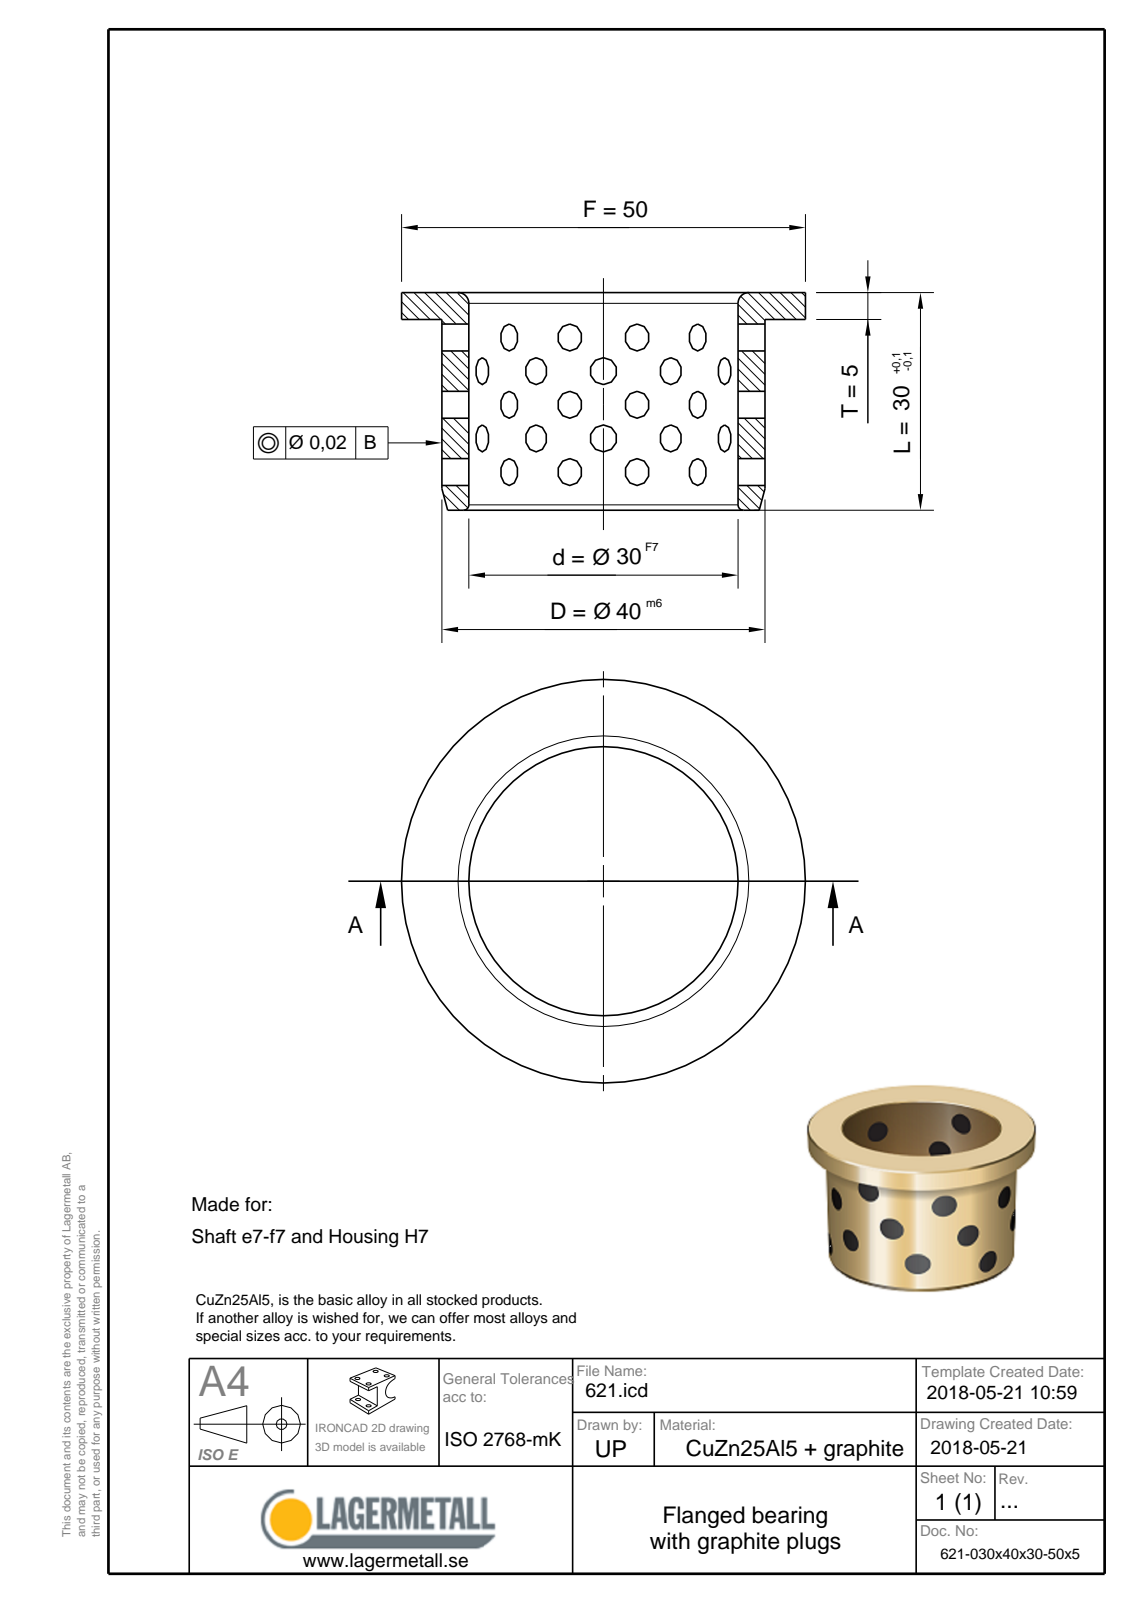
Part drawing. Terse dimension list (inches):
name: 621-030x40x30-50x5
written by: Spatial InterOp 3D (CONFIG_CONTROL_DESIGN)
unit: in
bodies: 1 solid, 9 faces (3 planar, 3 cylindrical, 3 other)
size: 1.969 × 1.969 × 1.181
volume: 1.21 in³; area: 14.02 in²
holes: 1× ⌀1.181
bosses: 1× ⌀1.969, 1× ⌀1.575
face distances: 0.197, 0.984, 1.181
